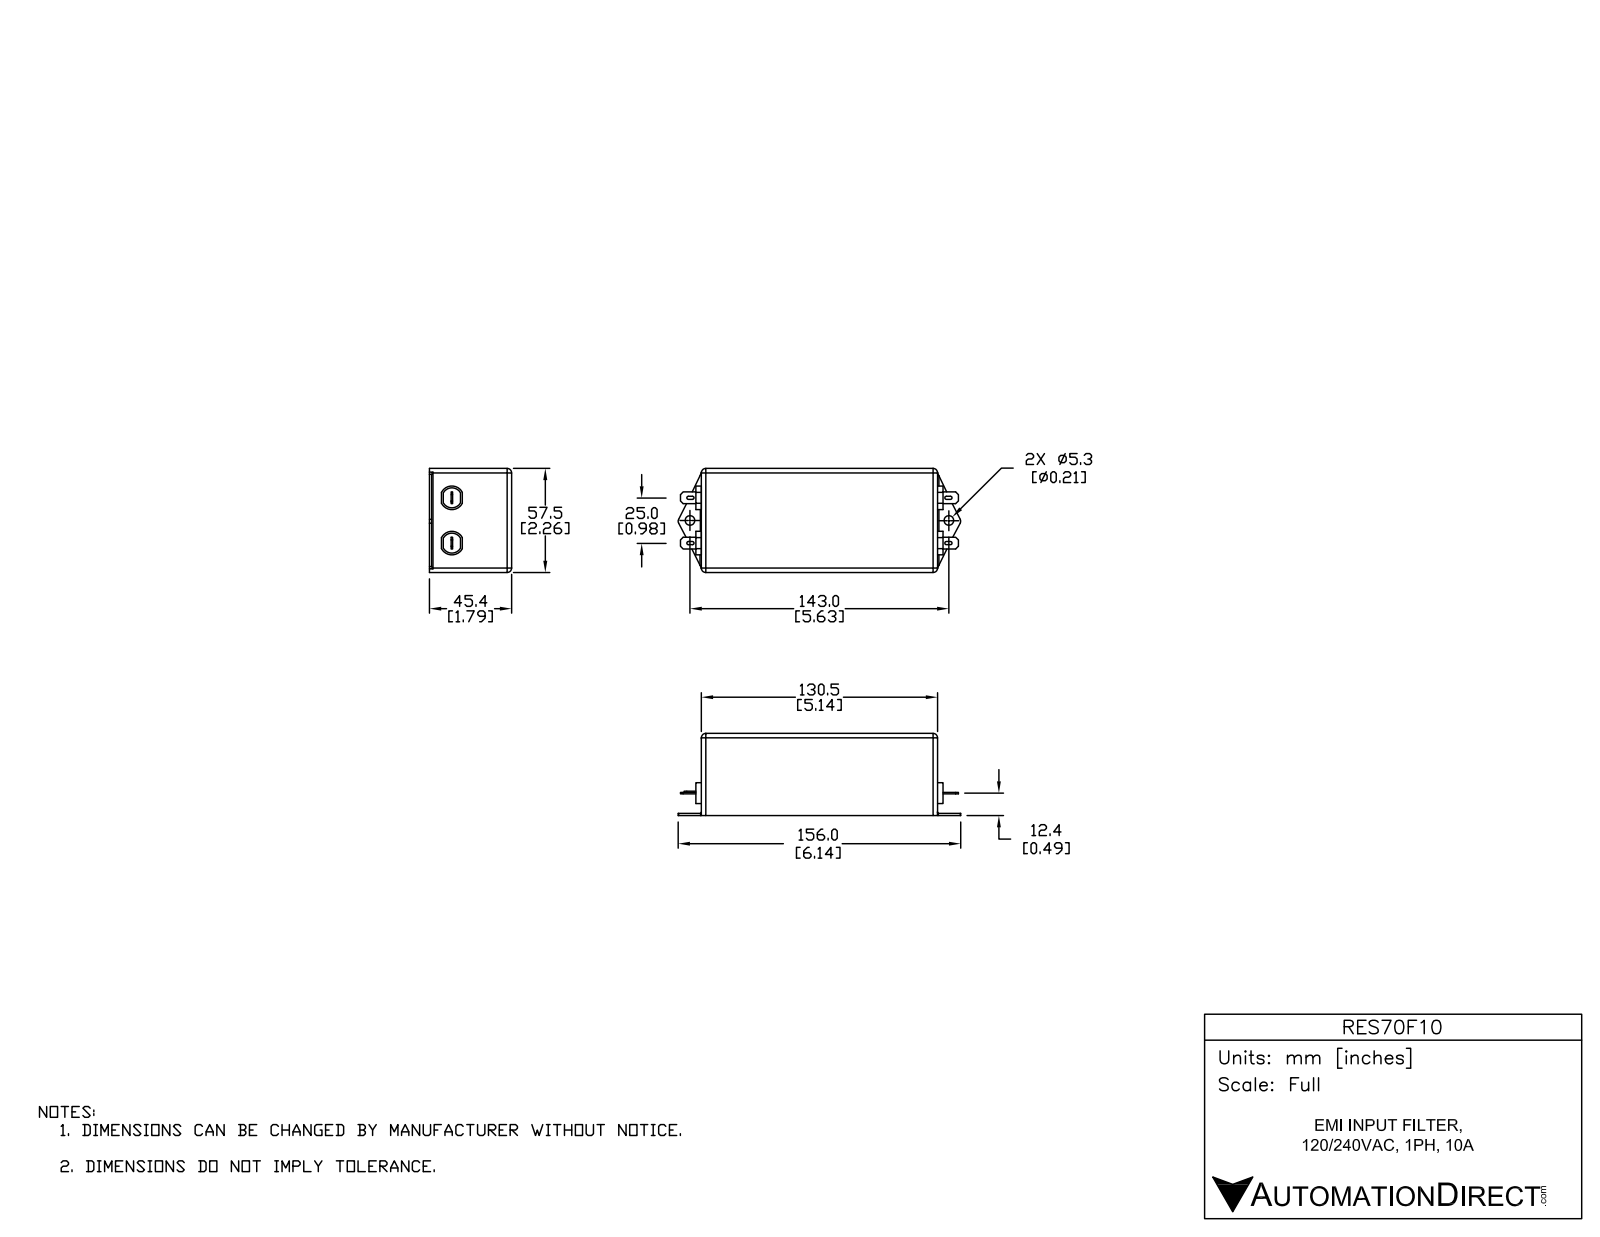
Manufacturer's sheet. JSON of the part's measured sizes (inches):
{"part_name": "RES70F10", "step_written_by": "SolidWorks 2015 (AUTOMOTIVE_DESIGN)", "units": "inches", "bodies": {"solids": 1, "faces": 133, "planar": 79, "cylindrical": 50, "other": 4}, "overall_size": [6.12, 2.264, 1.787], "volume_in3": 20.86, "surface_area_in2": 52.86, "round_holes": [[0.209, 2], [0.079, 1]], "partial_cylinders_radius": [[0.098, 10], [0.035, 8], [0.03, 2], [0.217, 2], [0.256, 2]], "face_to_face_distances": [1.787, 2.264, 5.138, 0.047, 1.74, 0.059, 5.197, 5.256, 0.031, 0.472], "hole_center_spacings": [5.63]}
